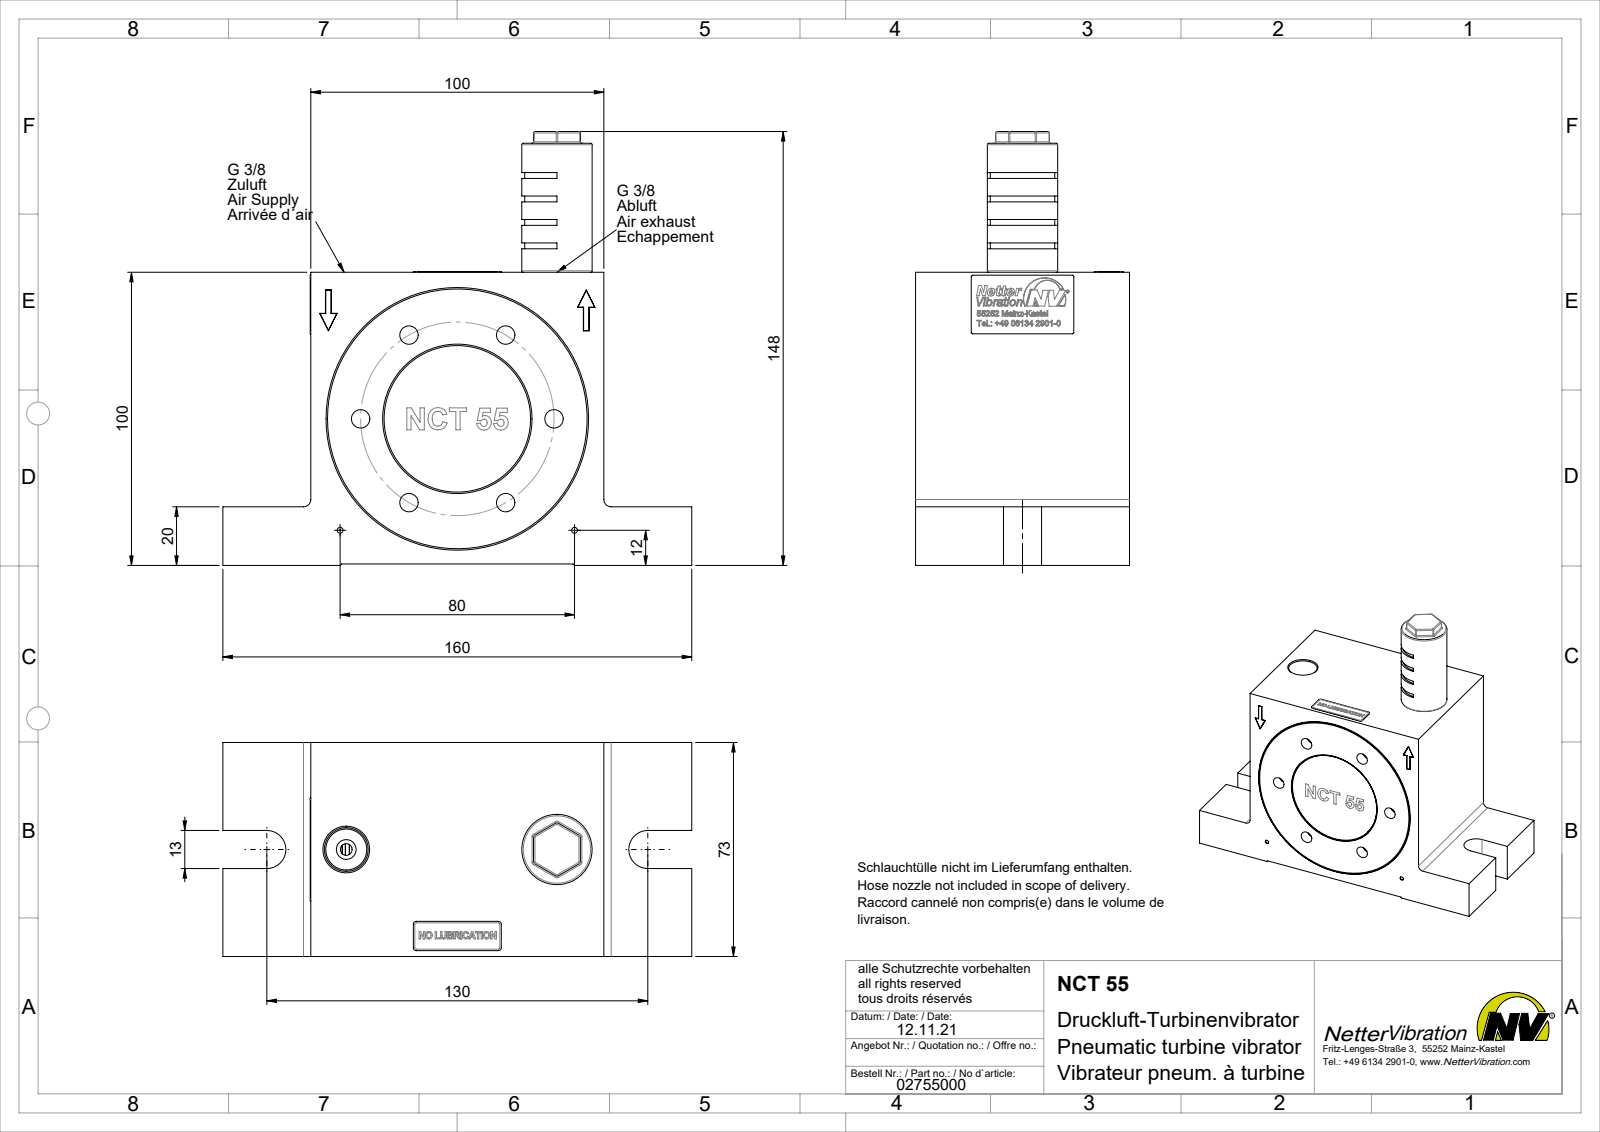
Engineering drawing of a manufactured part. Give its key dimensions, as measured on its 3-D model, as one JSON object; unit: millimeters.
{"part_name": "NCT 55 Turbinenvibrator #02755000", "step_written_by": "SolidWorks 2015 (AUTOMOTIVE_DESIGN)", "units": "millimeters", "bodies": {"solids": 2, "faces": 351, "planar": 209, "cylindrical": 81, "other": 61}, "overall_size": [160, 146, 73], "volume_mm3": 785487, "surface_area_mm2": 79115, "round_holes": [[6.3, 6], [2, 2], [15, 2], [40, 1], [51, 1], [52, 1], [87.5, 1], [88.4, 1]], "round_bosses_or_shafts": [[87.47, 1], [85.27, 1], [50, 1], [24, 1], [16.66, 1]], "partial_cylinders_radius": [[0.5, 22], [1, 4], [2.5, 2], [6.5, 2], [11, 1]], "face_to_face_distances": [100, 73, 0.5, 99.5, 30, 20, 19.5, 80, 54, 19], "hole_center_spacings": [33, 57.16, 66, 25.32, 38.64, 55.17, 57.28, 70.61]}
